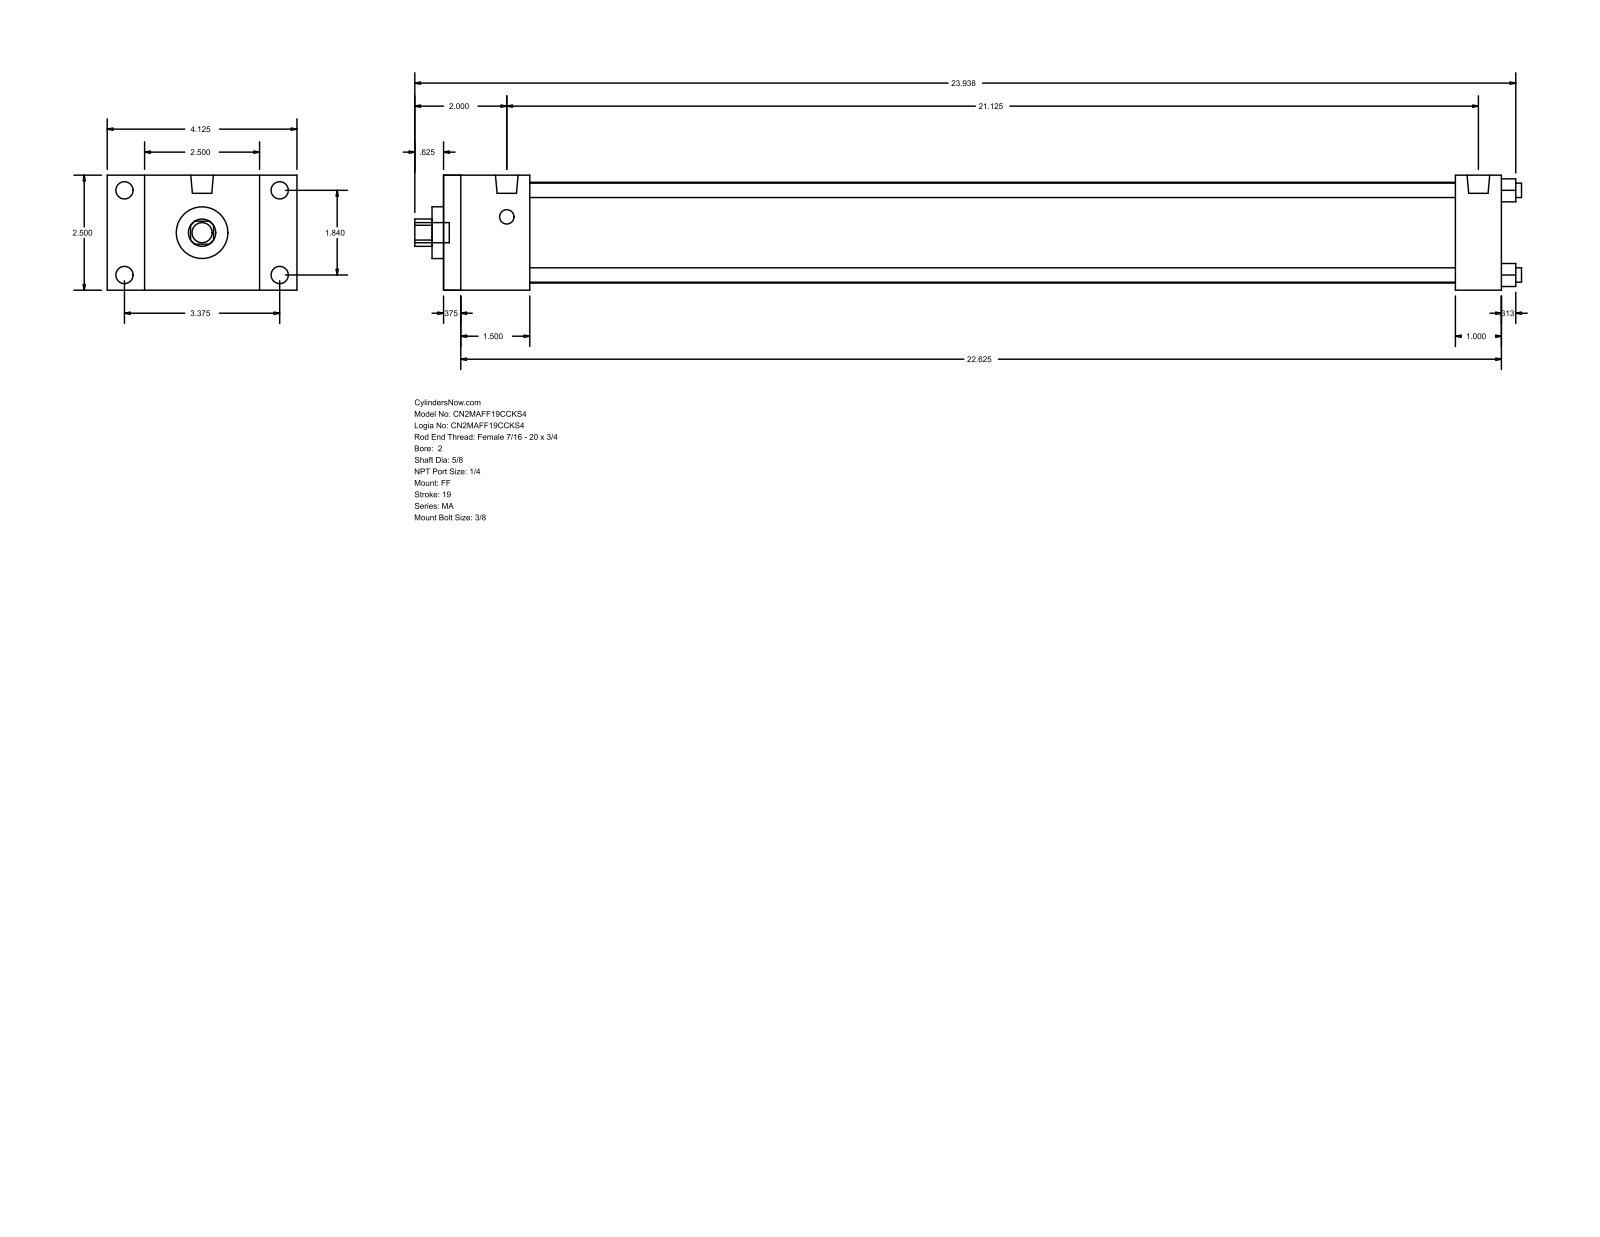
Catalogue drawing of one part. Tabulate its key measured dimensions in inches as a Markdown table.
| quantity | value |
| --- | --- |
| part name | MA_FF__0200_0.625 |
| STEP written by | GSSL Pune (CONFIG_CONTROL_DESIGN) |
| units | inches |
| bodies | 0 solids, 92 faces (64 planar, 28 cylindrical, 0 other) |
| overall size | 24.063 × 4.125 × 2.5 |
| round holes (diameter × count) | 0.313 × 4, 0.625 × 1, 1.125 × 1, 2.19 × 1 |
| round bosses / shafts (diameter × count) | 0.375 × 4, 0.313 × 4, 0.492 × 2, 0.437 × 1 |
| partial cylindrical surfaces (radius × count) | 0.297 × 1 |
| main face-to-face distances | 2.5, 23, 0.375, 22.625, 1.5, 1.875, 22, 21.625, 20.125, 21.125 |
| hole center spacings | 1.301, 1.84, 2.602 |
